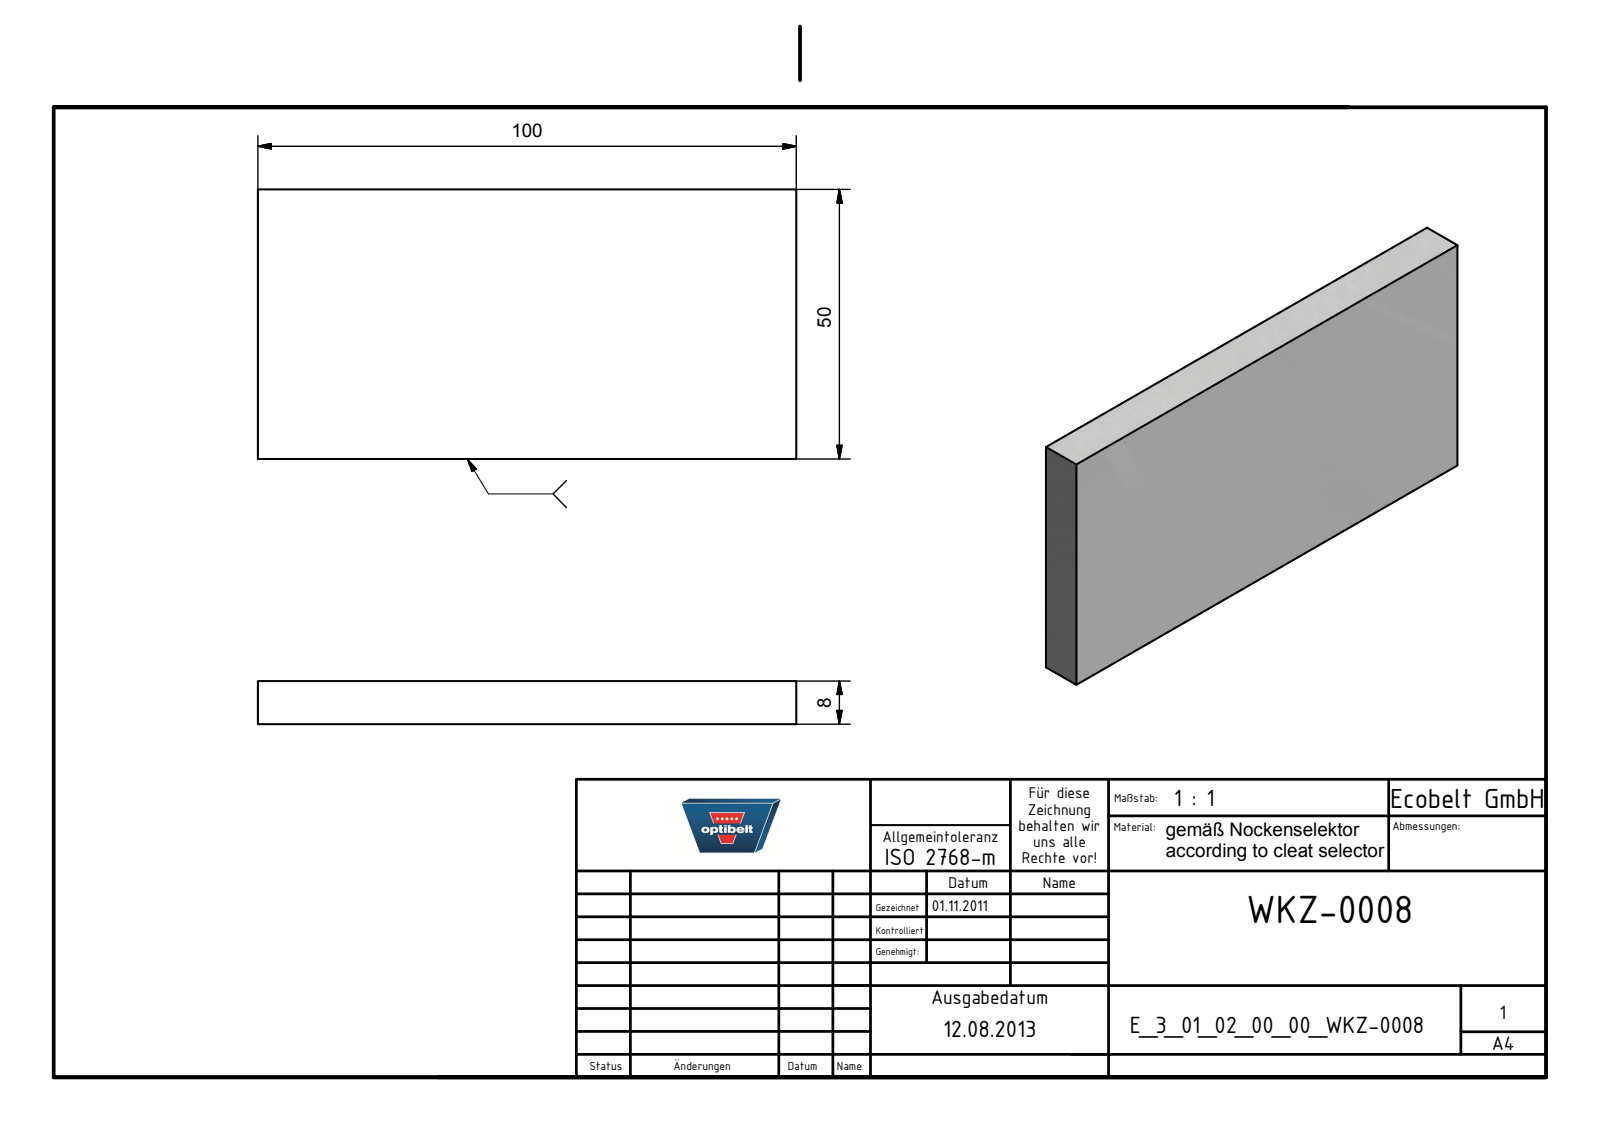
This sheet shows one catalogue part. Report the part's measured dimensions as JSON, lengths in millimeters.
{"part_name": "E_3_01_02_00_00_WKZ-0008", "step_written_by": "Autodesk Inventor 2021 (AUTOMOTIVE_DESIGN)", "units": "millimeters", "bodies": {"solids": 1, "faces": 6, "planar": 6, "cylindrical": 0, "other": 0}, "overall_size": [100, 50, 8], "volume_mm3": 40000, "surface_area_mm2": 12400, "face_to_face_distances": [8, 50, 100]}
